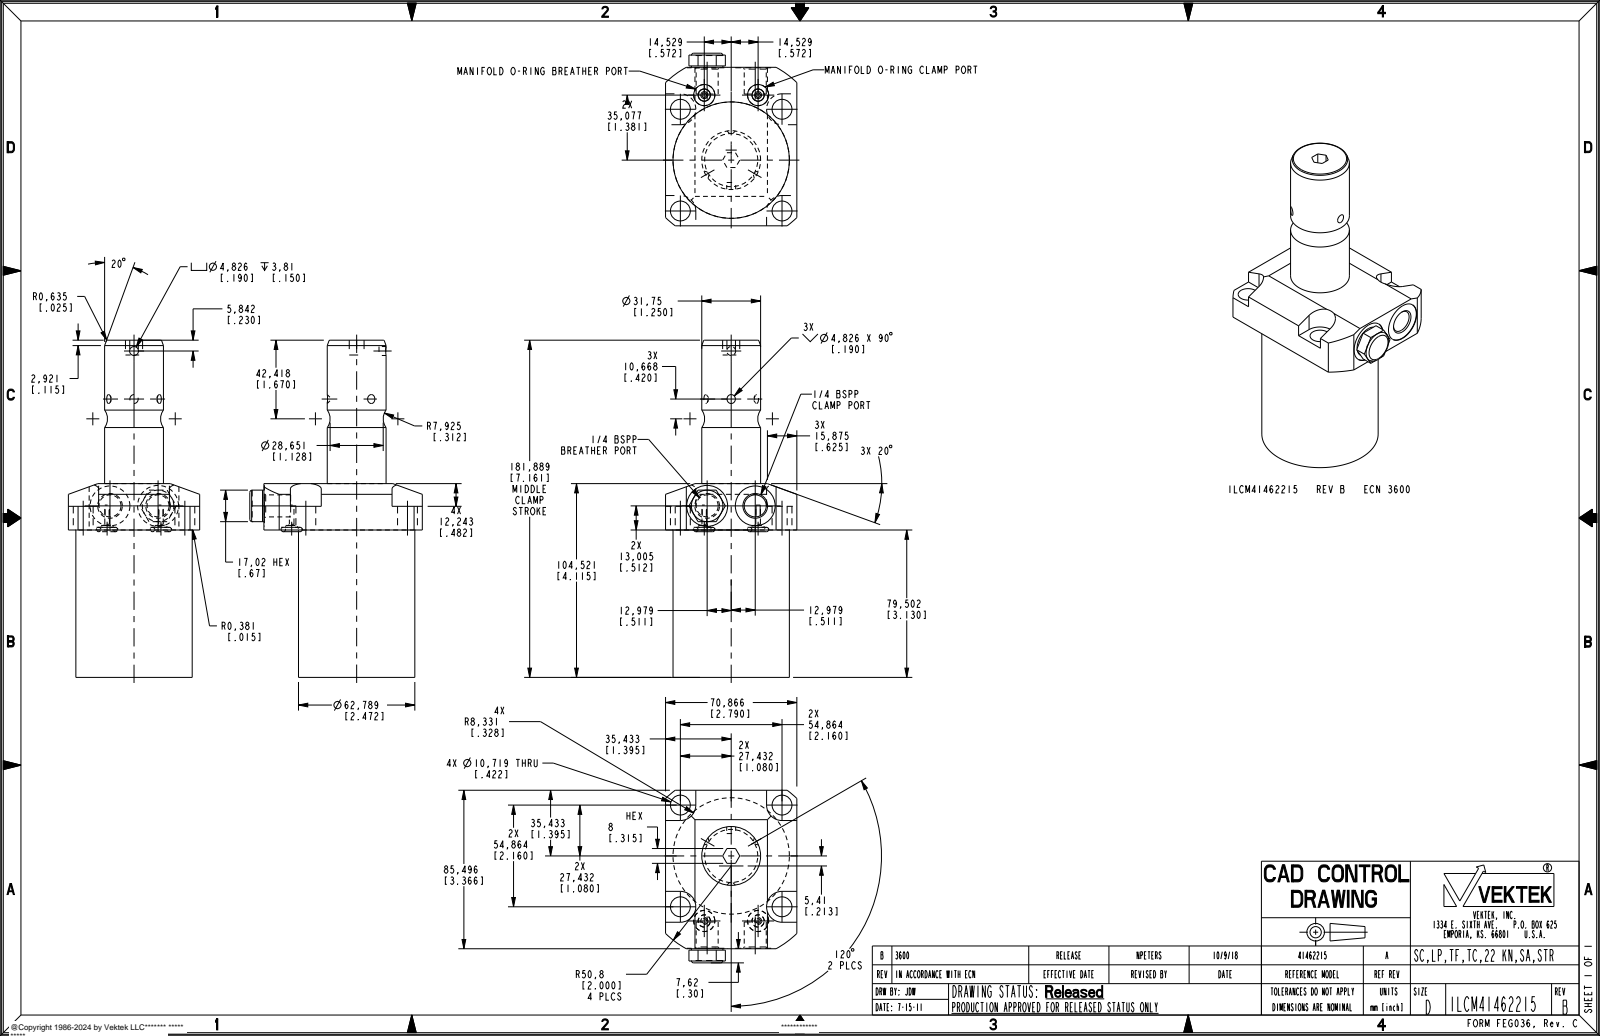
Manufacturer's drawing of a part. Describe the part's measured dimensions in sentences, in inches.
The part is named "ILCM41462215". Its 3-D file was written by "PRO/ENGINEER BY PARAMETRIC TECHNOLOGY CORPORATION, 2013320 (AUTOMOTIVE_DESIGN)". It is 3 solids with 143 faces: 63 planar, 48 cylindrical and 32 other. Overall it measures 7.161 by 3.666 by 2.79 inches. Its volume is 26.26 cubic inches and its surface area 71.17 square inches. Round holes: 4 of diameter 0.422, 2 of diameter 0.098, 2 of diameter 0.256, 2 of diameter 0.449, 2 of diameter 0.468, 1 of diameter 0.19, 1 of diameter 0.67, 1 of diameter 0.846, 1 of diameter 0.87. Round bosses or shafts: 1 of diameter 2.472, 1 of diameter 1.25. Partial cylindrical surfaces (rounded edges, fillets, slot ends): 4 of radius 0.328, 1 of radius 2. The main face-to-face distances are 3.13, 4.115, 0.985, 2.79, 3.633, 0.503, 0.482, 7.161, 4.031, 3.528. The hole center spacings are 2.16, 0.591, 1.679, 2.513, 2.964, 3.054, 3.328, 1.022.
